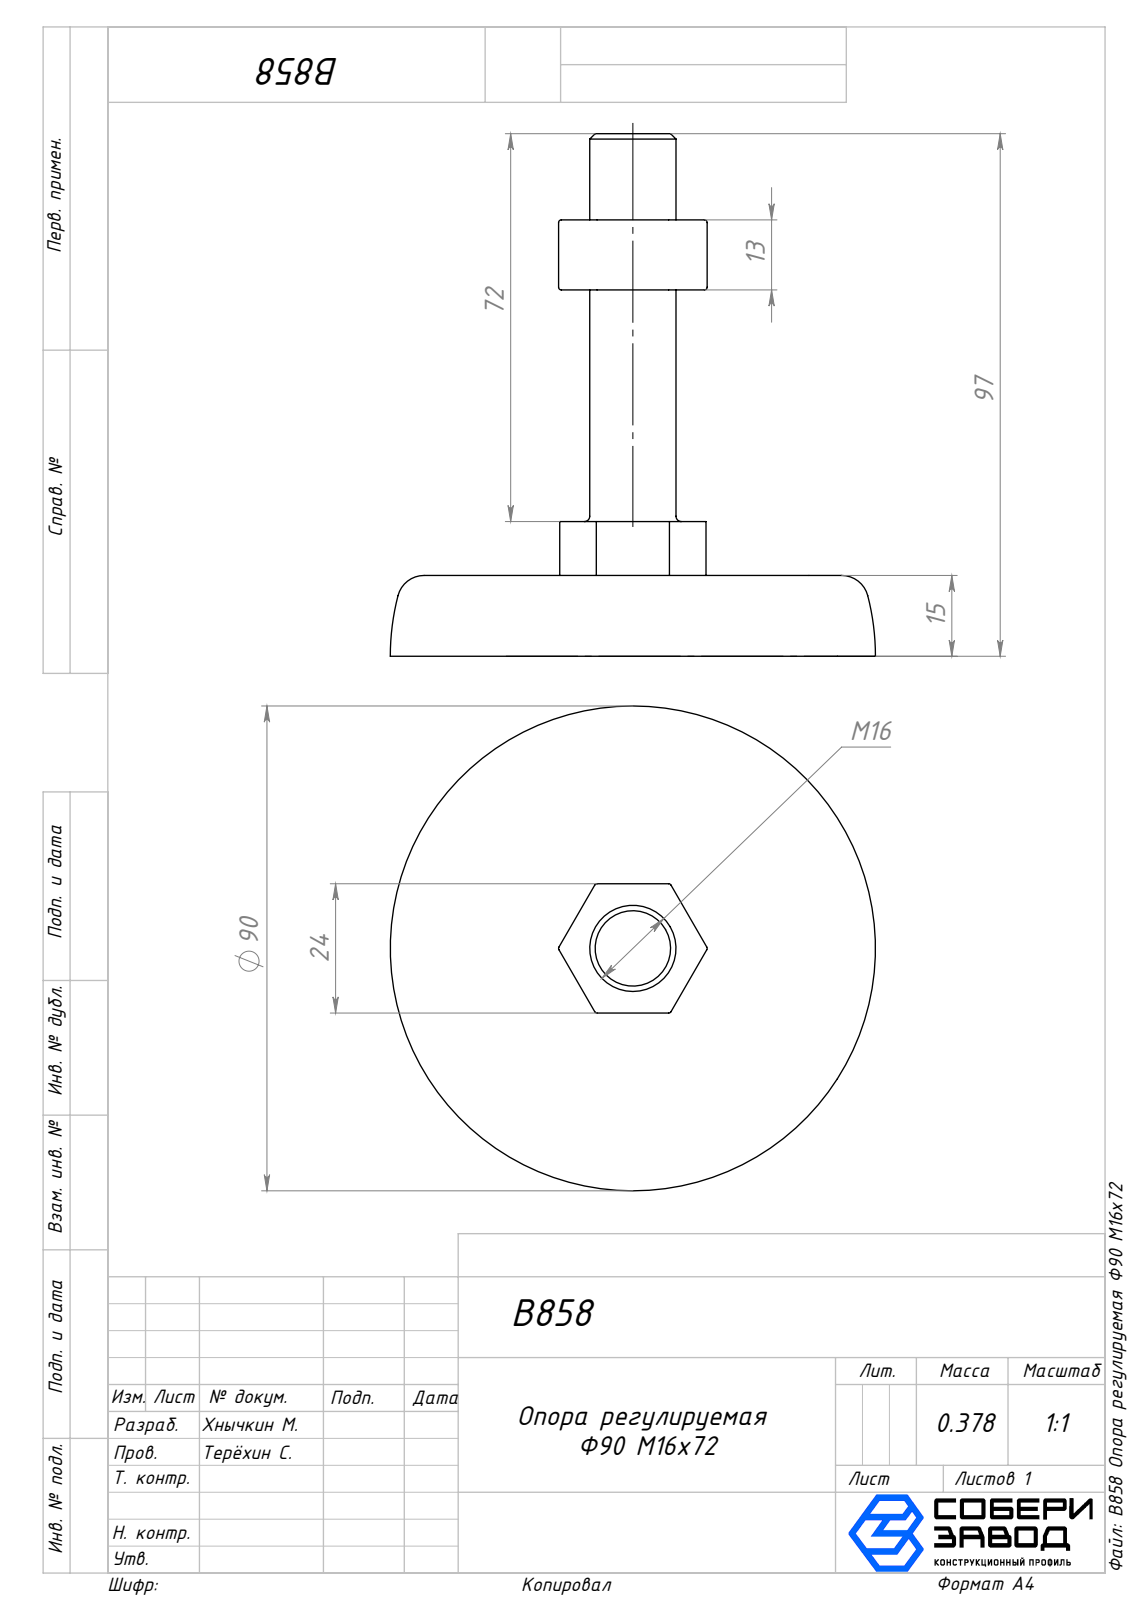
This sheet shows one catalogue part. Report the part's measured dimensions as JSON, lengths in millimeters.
{"part_name": "Гайка_00; Мал. гайка_00; Опора_00; B858 Опора регулируемая Ф90 М16х72 (+1 more)", "step_written_by": "SolidWorks 2025 (AUTOMOTIVE_DESIGN)", "units": "millimeters", "bodies": {"solids": 4, "faces": 120, "planar": 29, "cylindrical": 46, "other": 45}, "overall_size": [97, 90, 90], "volume_mm3": 40616, "surface_area_mm2": 27142, "round_holes": [[4, 1], [5, 1], [14, 1]], "round_bosses_or_shafts": [[16, 1]], "partial_cylinders_radius": [[0.5, 36]], "face_to_face_distances": [14.8, 15, 23.75, 24, 23.5, 10, 81, 66.2, 66, 68]}
